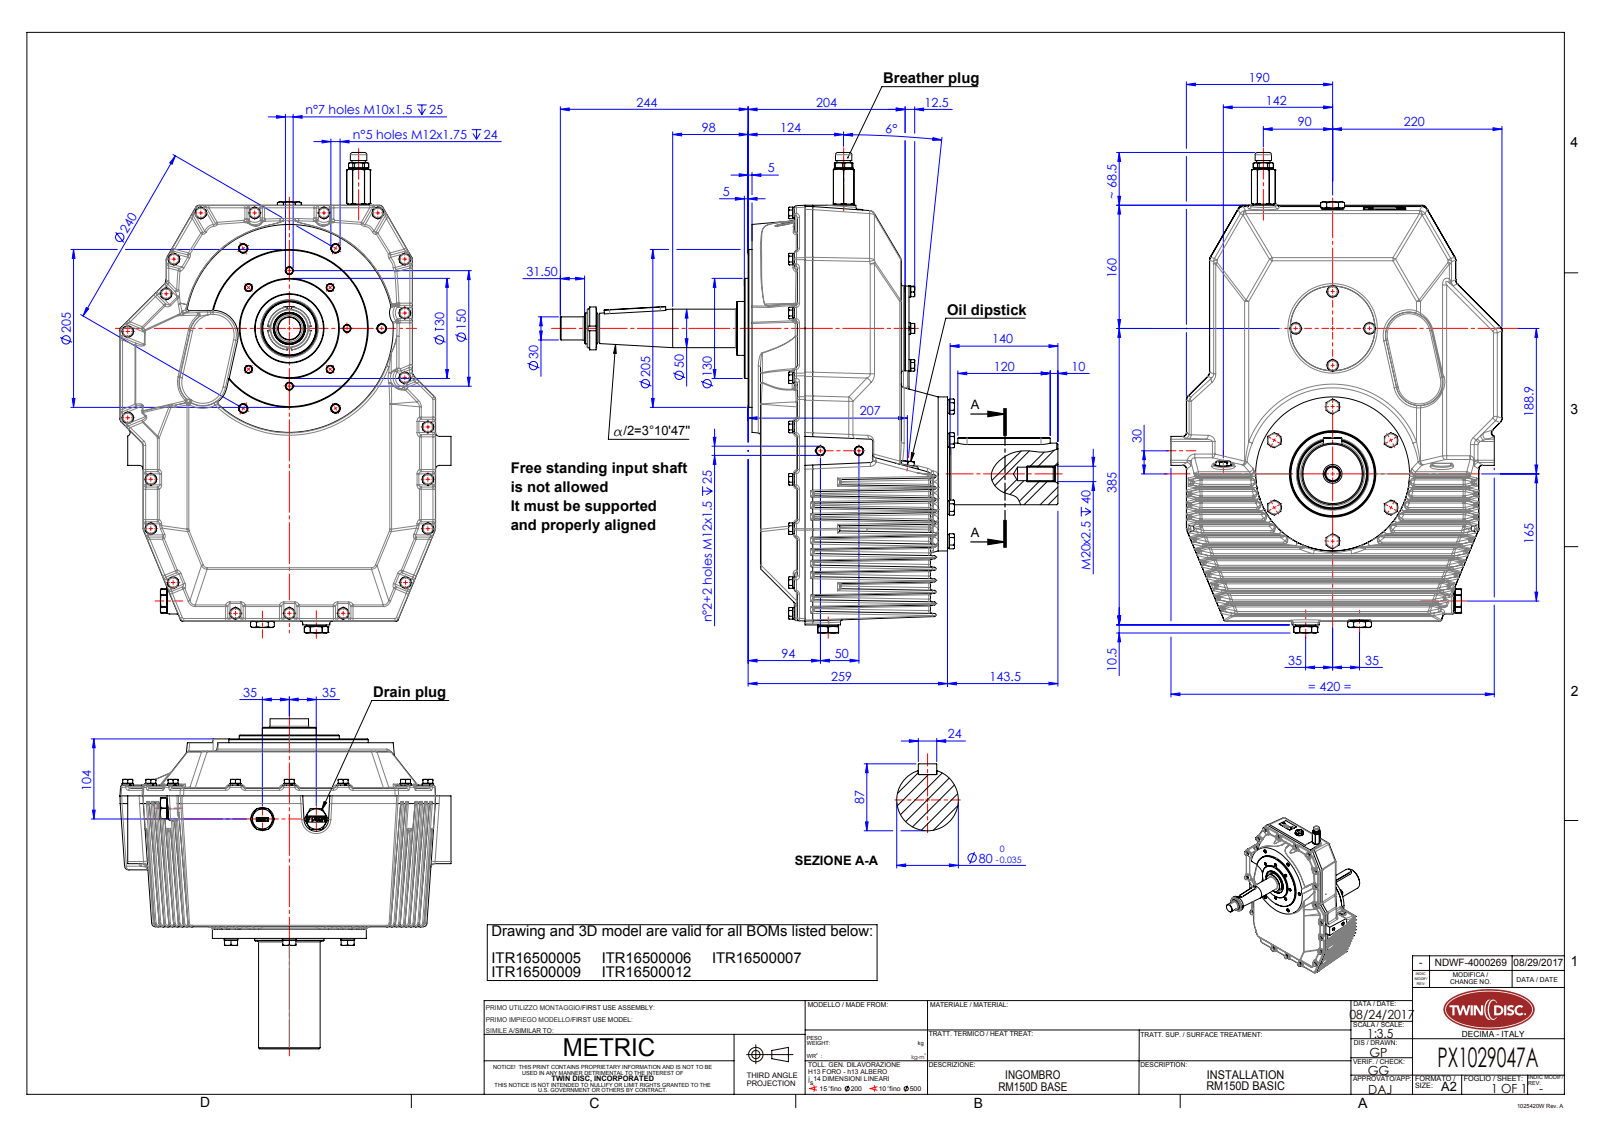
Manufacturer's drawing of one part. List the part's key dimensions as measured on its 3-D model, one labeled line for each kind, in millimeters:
Part name (STEP PRODUCT): ITrm120-003_rev00-installation; IT4588002_rev00-installation; IT4580002_Semplice; IT4620109 (+5 more)
STEP written by: SolidWorks 2015 (AUTOMOTIVE_DESIGN)
Units: millimetres
Bodies: 11 solids, 4741 faces (1674 planar, 1511 cylindrical, 1556 other)
Overall size (bounding box): 646.5 × 624 × 430
Volume: 3 681 000 mm³ · Surface area: 1 468 000 mm²
Round holes (diameter × count): ⌀8.5 ×34, ⌀6.8 ×25, ⌀8.2 ×21, ⌀10.2 ×13, ⌀12 ×8, ⌀10 ×7, ⌀11 ×6, ⌀18.5 ×4, ⌀20 ×3, ⌀18.63 ×2, ⌀21 ×2, ⌀30 ×2
Round bosses / shafts (diameter × count): ⌀14.8 ×25, ⌀12.2 ×25, ⌀8 ×25, ⌀18.1 ×6, ⌀16.2 ×6, ⌀10 ×6, ⌀26 ×3, ⌀27 ×2
Partial cylindrical surfaces — rounded edges, fillets, slot ends (radius × count): R3 ×161, R2 ×121, R2.5 ×74, R5 ×47, R8 ×41, R1.5 ×4, R4.5 ×4, R10 ×4
Main face-to-face distances: 5, 10, 135, 60, 204, 30, 209, 199, 15, 69
Hole centre spacings: 120, 75, 57.4, 138.58, 70, 51.37, 66.61, 106.06
